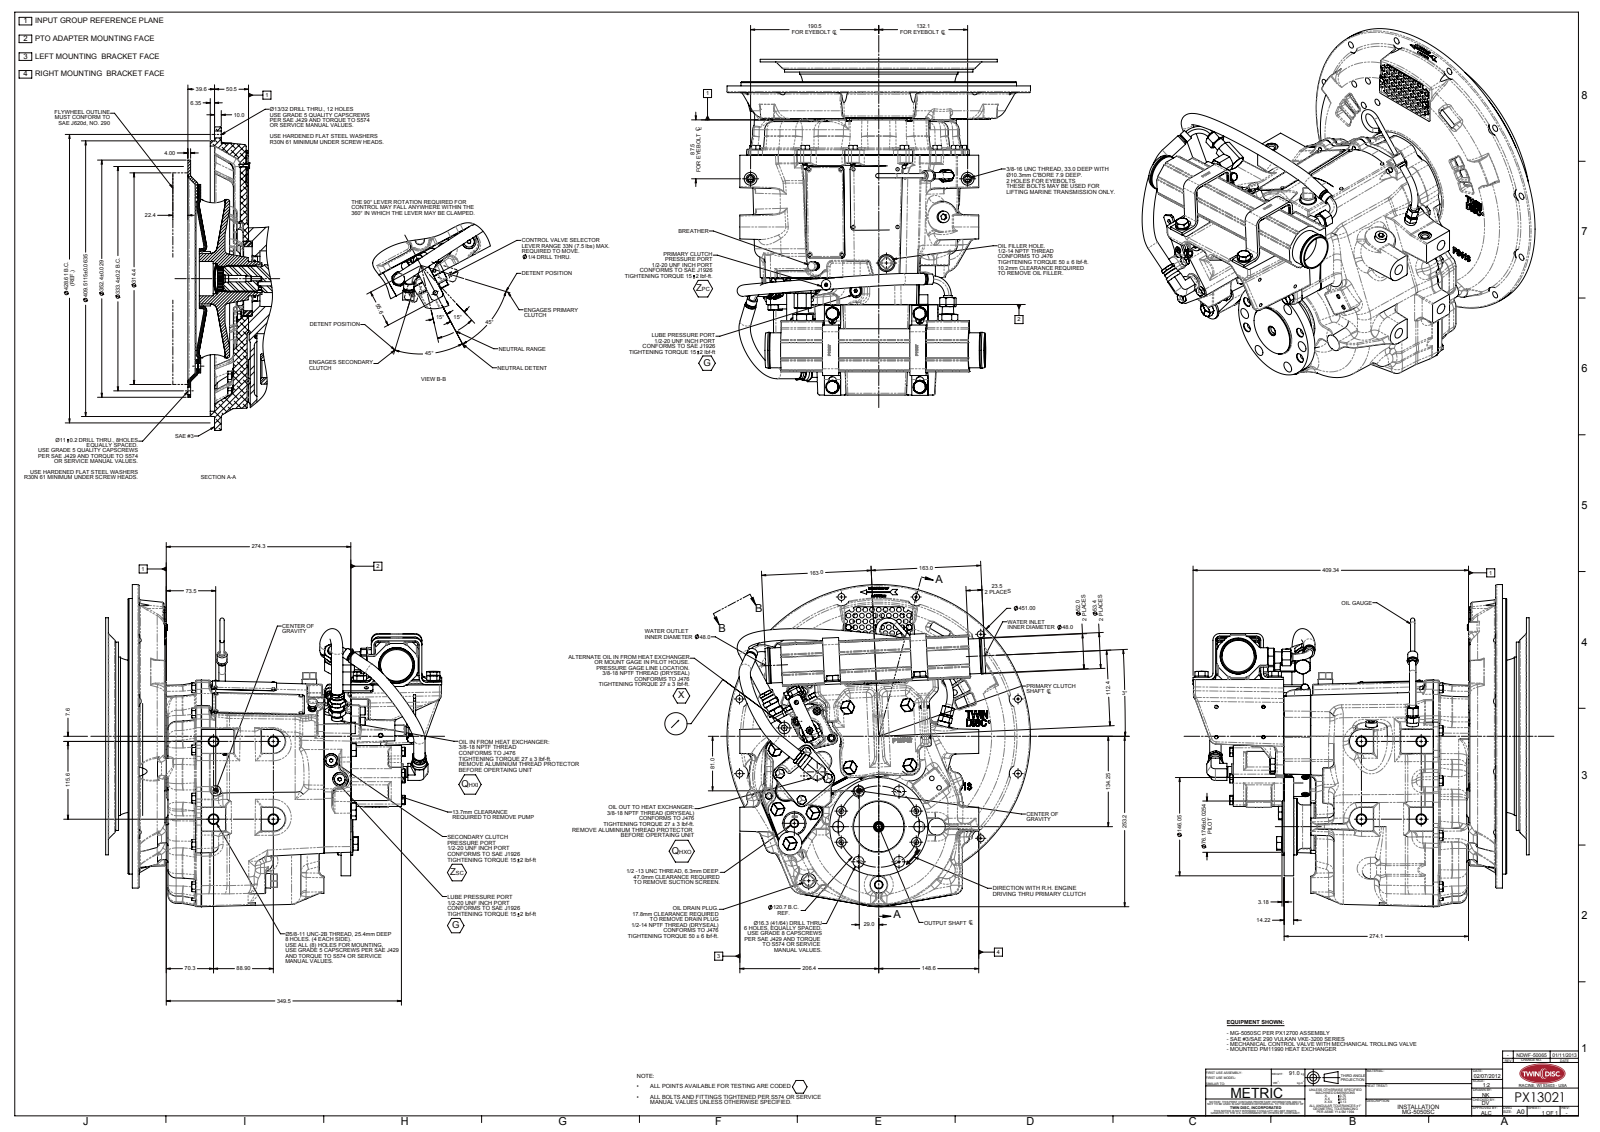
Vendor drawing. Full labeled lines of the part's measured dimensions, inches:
Part name (STEP PRODUCT): PX13021
STEP written by: SolidWorks 2010 (AUTOMOTIVE_DESIGN)
Units: inches
Bodies: 0 solids, 4307 faces (1102 planar, 1244 cylindrical, 1961 other)
Overall size (bounding box): 19.661 × 18.848 × 17.756
Round holes (diameter × count): ⌀0.276 ×51, ⌀0.406 ×14, ⌀0.323 ×12, ⌀0.433 ×8, ⌀0.313 ×6, ⌀0.641 ×6, ⌀0.197 ×4, ⌀0.281 ×4, ⌀0.406 ×4, ⌀0.563 ×4, ⌀0.813 ×3, ⌀0.165 ×2
Round bosses / shafts (diameter × count): ⌀0.743 ×5, ⌀0.781 ×4, ⌀0.665 ×4, ⌀0.625 ×4, ⌀0.494 ×4, ⌀0.25 ×4, ⌀0.599 ×3, ⌀0.469 ×3
Partial cylindrical surfaces — rounded edges, fillets, slot ends (radius × count): R0.059 ×97, R0.06 ×62, R0.32 ×61, R0.315 ×52, R0.016 ×32, R0.098 ×30, R0.118 ×27, R0.512 ×24
Main face-to-face distances: 0.157, 9.303, 0.591, 0.026, 9.329, 9.15, 9.124, 0.179, 0.433, 7.184
Hole centre spacings: 8.437, 8.437, 14.614, 0.394, 4.367, 11.932, 16.3, 0.787
